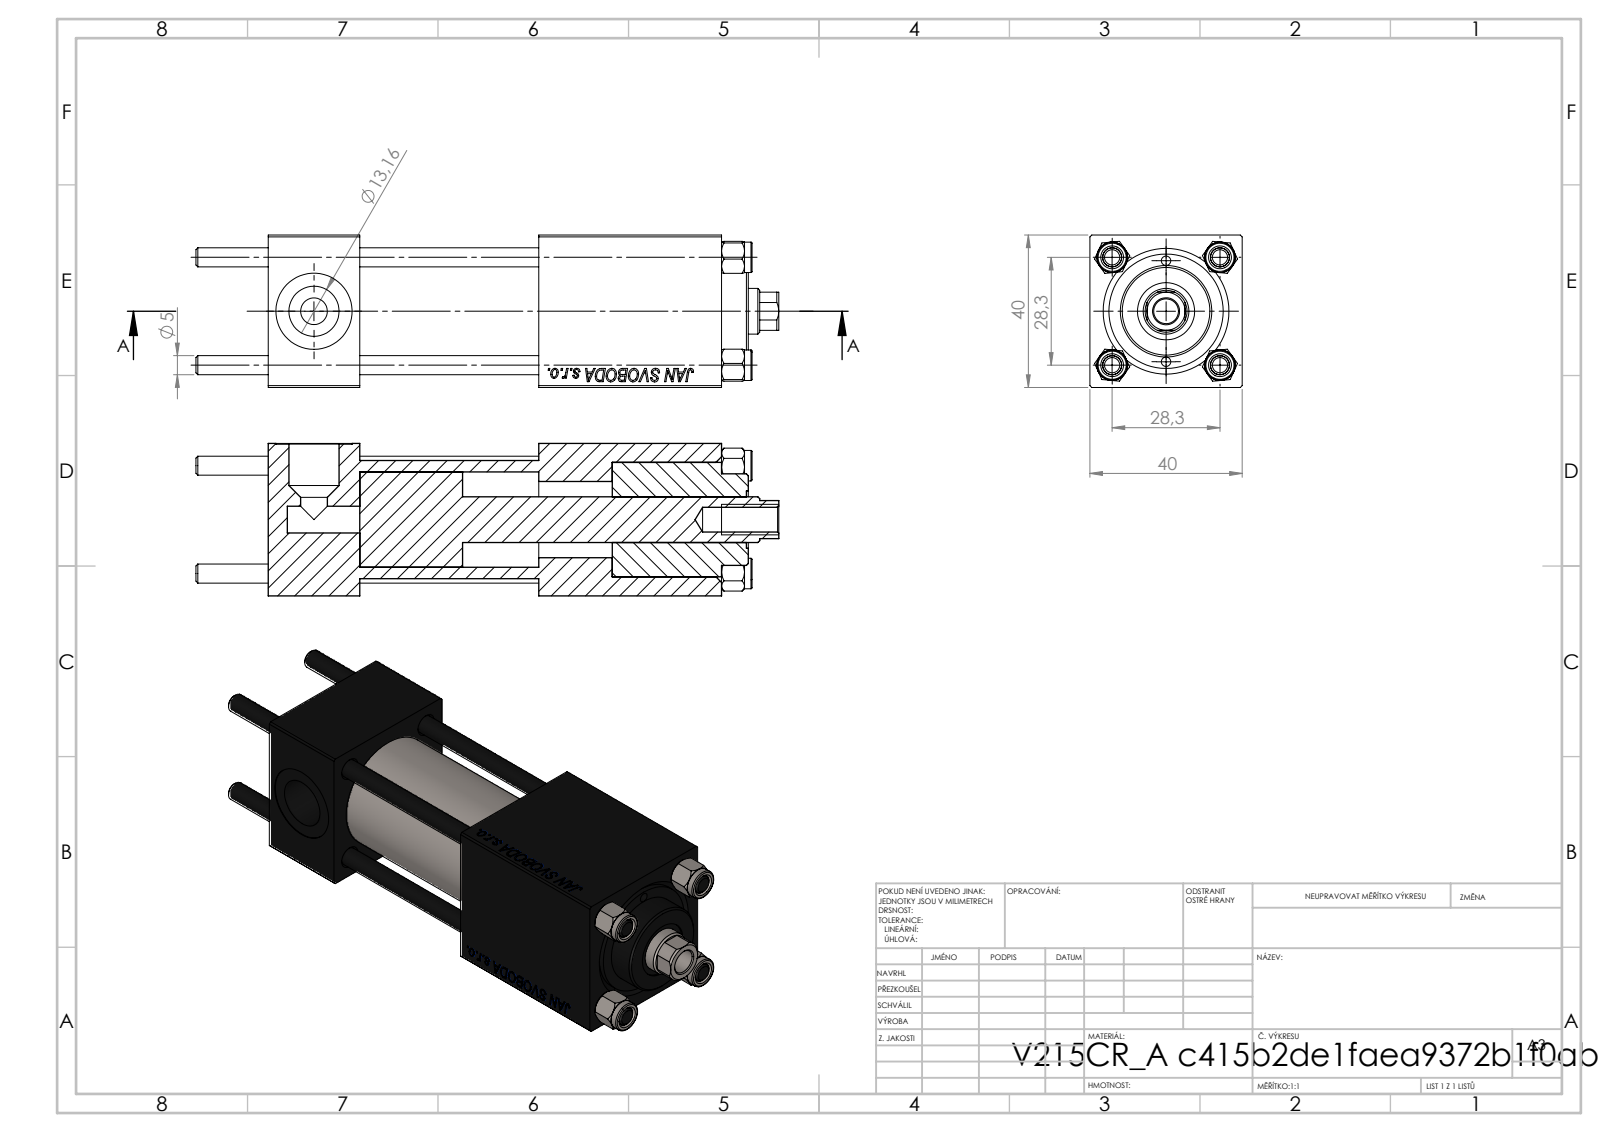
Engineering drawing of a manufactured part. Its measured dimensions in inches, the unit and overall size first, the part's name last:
Units: inches
Overall size (bounding box): 6.024 × 1.575 × 1.575
Round holes (diameter × count): ⌀0.197 ×4, ⌀0.787 ×3, ⌀0.098 ×2, ⌀0.276 ×2, ⌀0.518 ×2, ⌀0.256 ×1, ⌀0.472 ×1, ⌀0.591 ×1, ⌀0.984 ×1, ⌀1.181 ×1
Round bosses / shafts (diameter × count): ⌀0.315 ×4, ⌀1.22 ×1, ⌀0.945 ×1
Partial cylindrical surfaces — rounded edges, fillets, slot ends (radius × count): R0.217 ×1
Main face-to-face distances: 1.575, 0.945, 3.555, 2.61, 4.685, 3.74, 1.13, 2.795, 1.85, 0.76
Hole centre spacings: 0.558, 0.788, 1.114, 1.214, 0.522, 1.576, 1.043
Volume: 8.83 in³ · Surface area: 91.37 in²
Bodies: 11 solids, 1138 faces (519 planar, 83 cylindrical, 536 other)
Part name (STEP PRODUCT): V215_VC_A; V215CR_BODY_A; V215CR_VCP; CR025_012_A_0_G_A_G_M_020_+#_##_TYCINKA (+1 more)
STEP written by: SolidWorks 2019 (CONFIG_CONTROL_DESIGN)
